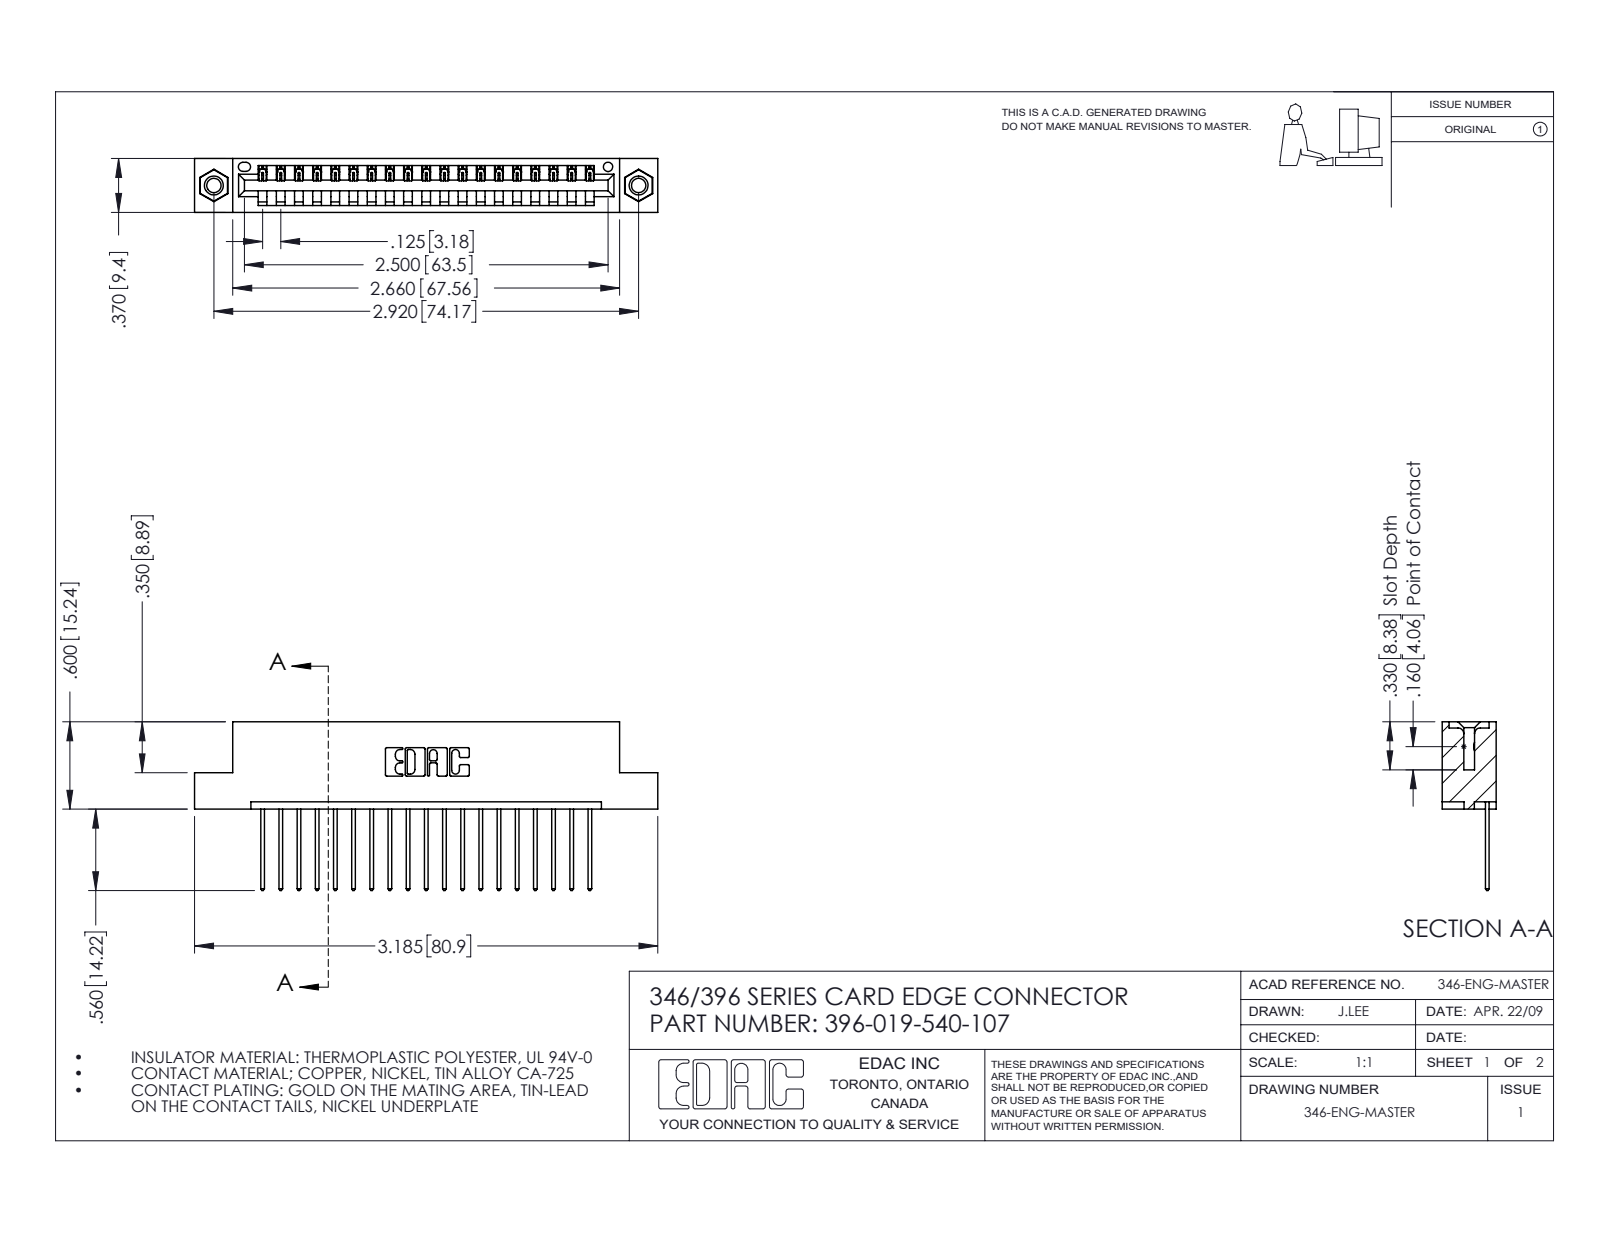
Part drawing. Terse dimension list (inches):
name: 345-292-001_345-293-140; 345-250-001_345-250-005-103; 396-019-540-107; 346 Part_Flush Mounting Lugs - 0.156 Dia-TI
written by: SolidWorks 2016 (CONFIG_CONTROL_DESIGN)
unit: in
bodies: 22 solids, 1284 faces (868 planar, 400 cylindrical, 16 other)
size: 3.185 × 1.16 × 0.37
volume: 0.464 in³; area: 14.68 in²
holes: 2× ⌀0.098, 2× ⌀0.125, 2× ⌀0.156, 1× ⌀0.064
bosses: 2× ⌀0.155
rounds: 38× R0.006, 38× R0.01, 22× R0.01, 6× R0.007, 6× R0.031, 3× R0.026, 2× R0.031, 2× R0.04
face distances: 0.048, 0.322, 0.25, 0.37, 0.072, 0.298, 0.025, 0.148, 0.222, 0.1
hole spacings: 0.246, 2.713, 2.92
